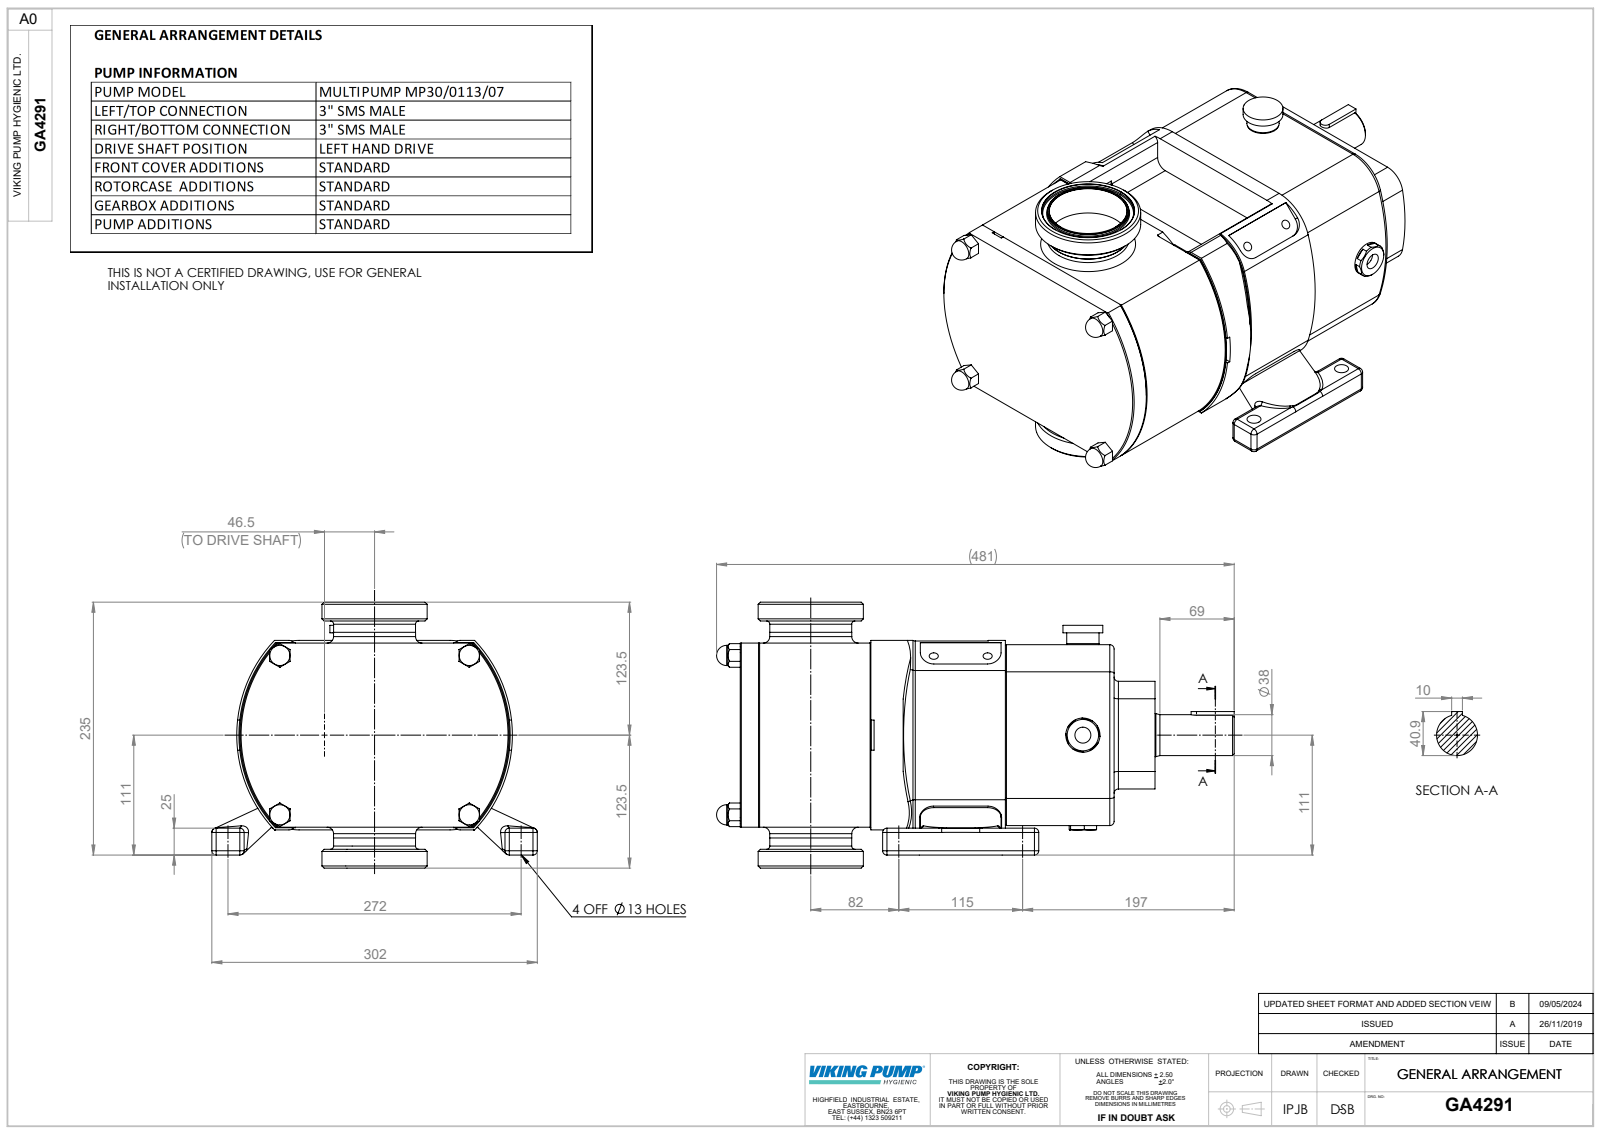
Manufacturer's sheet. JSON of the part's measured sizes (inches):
{"part_name": "GA4291; Copy of CP30-0113-07 V L^GA4291; Copy of Z94-5101-55 - 3 INCH SMS681^GA4291", "step_written_by": "SolidWorks 2023 (AUTOMOTIVE_DESIGN)", "units": "inches", "bodies": {"solids": 3, "faces": 751, "planar": 271, "cylindrical": 250, "other": 230}, "overall_size": [18.93, 11.902, 9.724], "volume_in3": 792.7, "surface_area_in2": 885.8, "round_holes": [[0.335, 4], [0.398, 4], [0.512, 4], [0.358, 2], [0.585, 1], [1.378, 1], [2.843, 1], [3.386, 1]], "round_bosses_or_shafts": [[0.74, 4], [3.268, 2], [1.969, 2], [3.846, 1], [3, 1], [2.996, 1], [2.972, 1], [1.575, 1]], "partial_cylinders_radius": [[0.157, 44], [0.039, 16], [0.394, 12], [0.236, 10], [0.492, 4], [0.495, 4], [0.496, 4], [0.787, 4]], "face_to_face_distances": [0.059, 6.673, 1.496, 5.472, 6.702, 8.467, 15.169, 6.732, 1.142, 1.201], "hole_center_spacings": [2.506, 1.97, 3.399, 3.543, 3.548, 4.528, 6.025, 6.253]}
